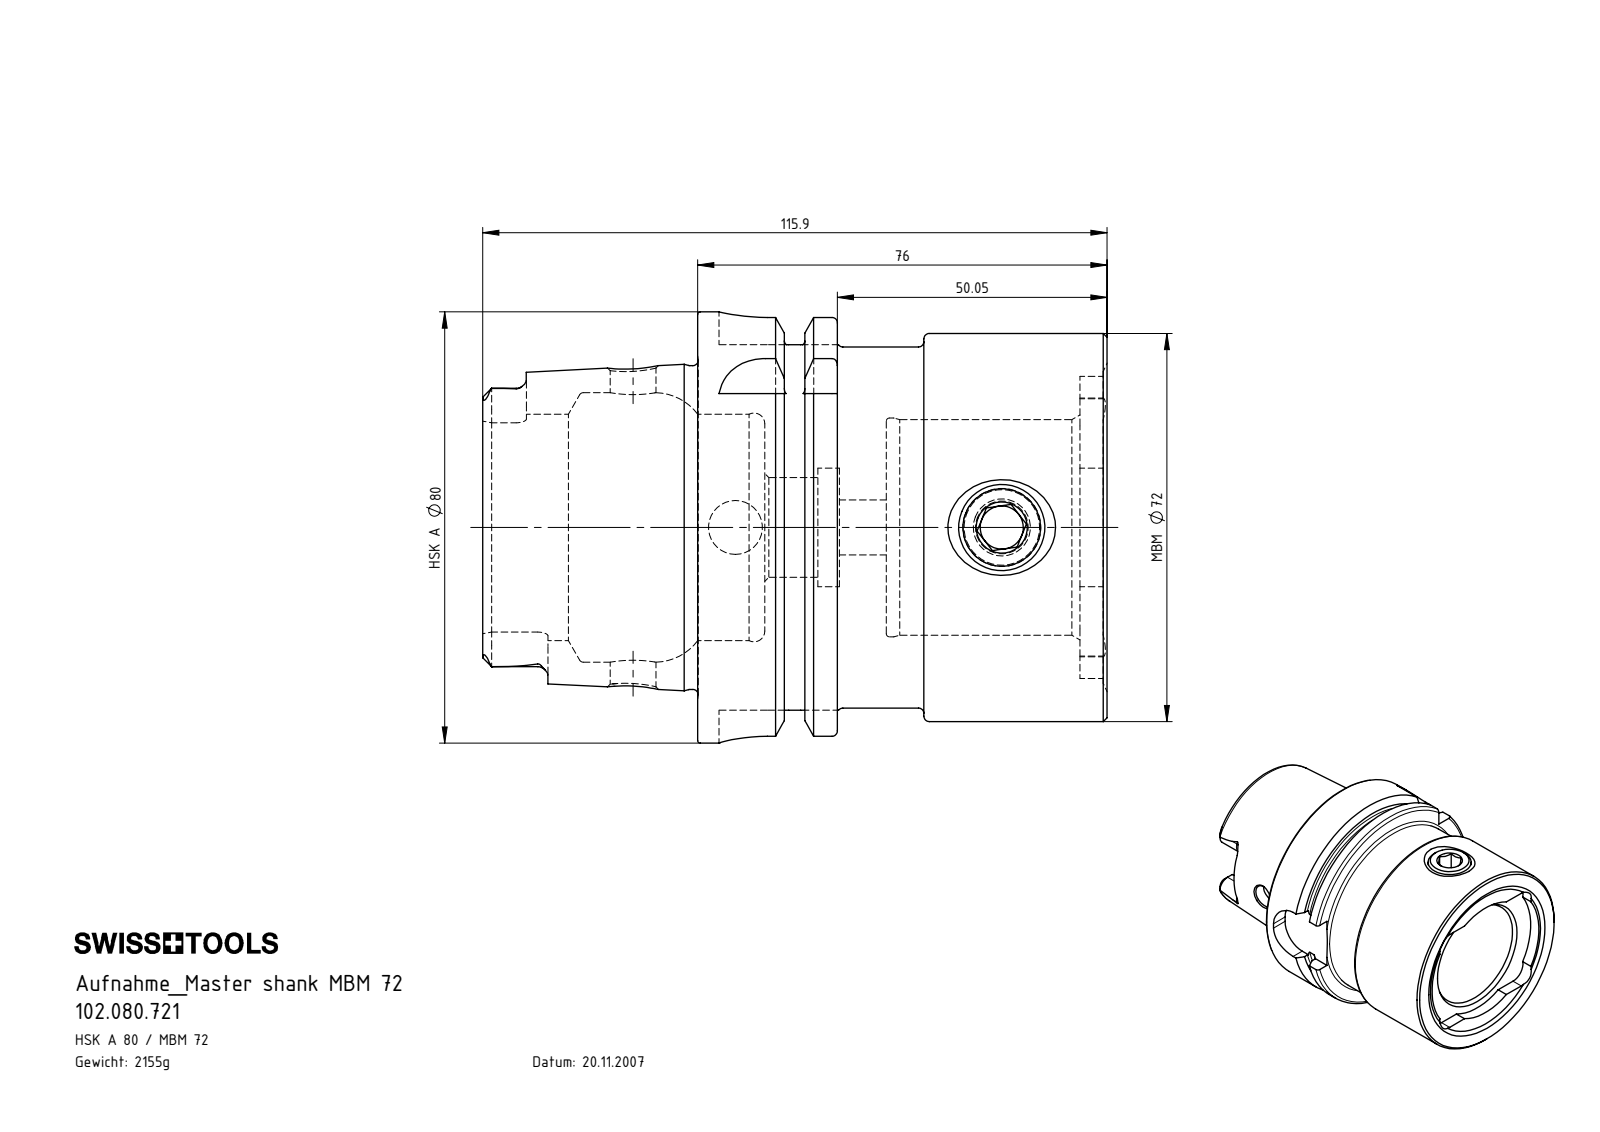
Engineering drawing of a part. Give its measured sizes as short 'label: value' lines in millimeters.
name: MB7-ER1.001.022_A; HA8-MB7.K01.076_B_Fertigbearbeitung; 102.080.721
written by: SolidWorks 2017 (CONFIG_CONTROL_DESIGN)
unit: mm
bodies: 2 solids, 229 faces (72 planar, 68 cylindrical, 89 other)
size: 115.9 × 80 × 80
volume: 274 577 mm³; area: 52 398 mm²
holes: 1× ⌀8, 1× ⌀8.5, 1× ⌀10, 1× ⌀10.2, 1× ⌀14.5, 1× ⌀18.5, 1× ⌀22, 1× ⌀40, 1× ⌀40.6, 1× ⌀42, 1× ⌀50
bosses: 1× ⌀80, 1× ⌀72, 1× ⌀69.95, 1× ⌀67, 1× ⌀60.06, 1× ⌀16
rounds: 6× R1.9, 4× R3.88, 4× R5.2, 4× R9, 1× R23.75, 1× R28.02
face distances: 35, 76, 41, 9.05, 45, 70.95, 35.95, 5.05, 25.95, 50.05
hole spacings: 49.45
